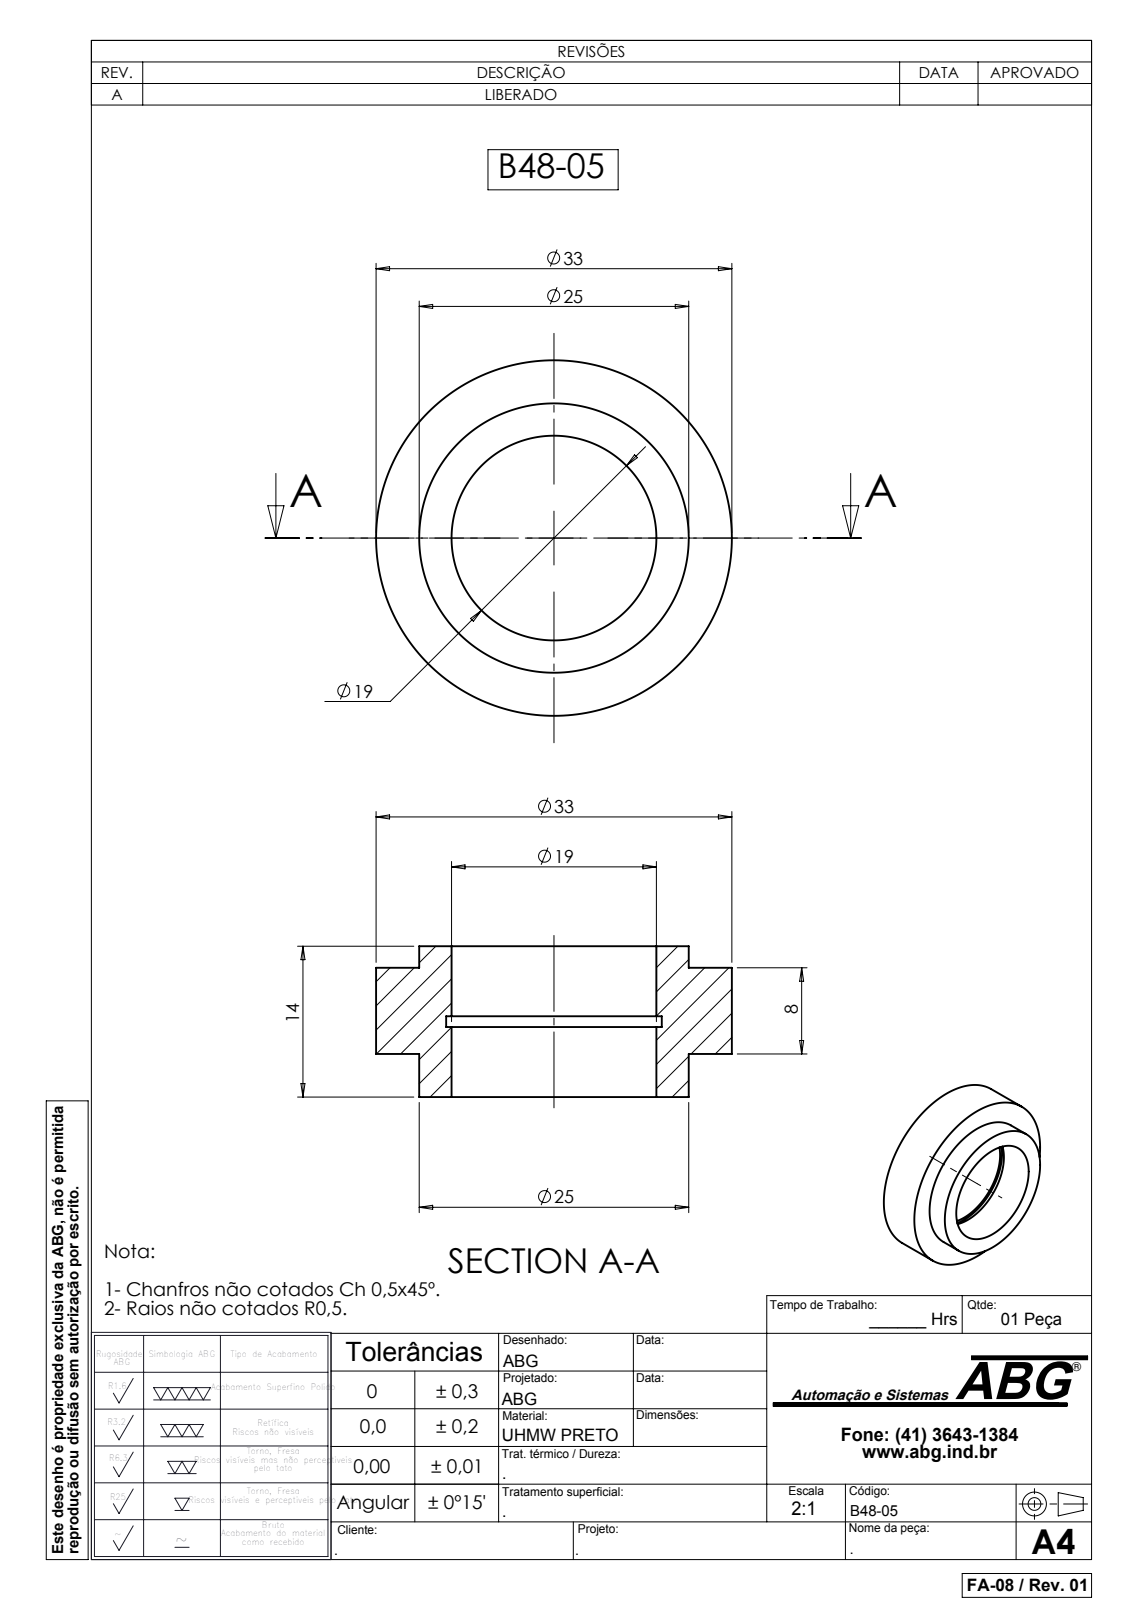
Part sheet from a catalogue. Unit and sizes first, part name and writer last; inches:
Units: inches
Overall size (bounding box): 1.299 × 1.299 × 0.551
Round holes (diameter × count): ⌀0.748 ×1, ⌀0.787 ×1
Round bosses / shafts (diameter × count): ⌀1.299 ×1, ⌀0.984 ×1
Main face-to-face distances: 0.315, 0.472, 0.157, 0.079, 0.394, 0.551, 0.256, 0.295, 0.177, 0.217
Volume: 0.353 in³ · Surface area: 5.183 in²
Bodies: 1 solid, 18 faces (6 planar, 12 cylindrical, 0 other)
Part name (STEP PRODUCT): B48-05
STEP written by: SolidWorks 2007 (CONFIG_CONTROL_DESIGN)
